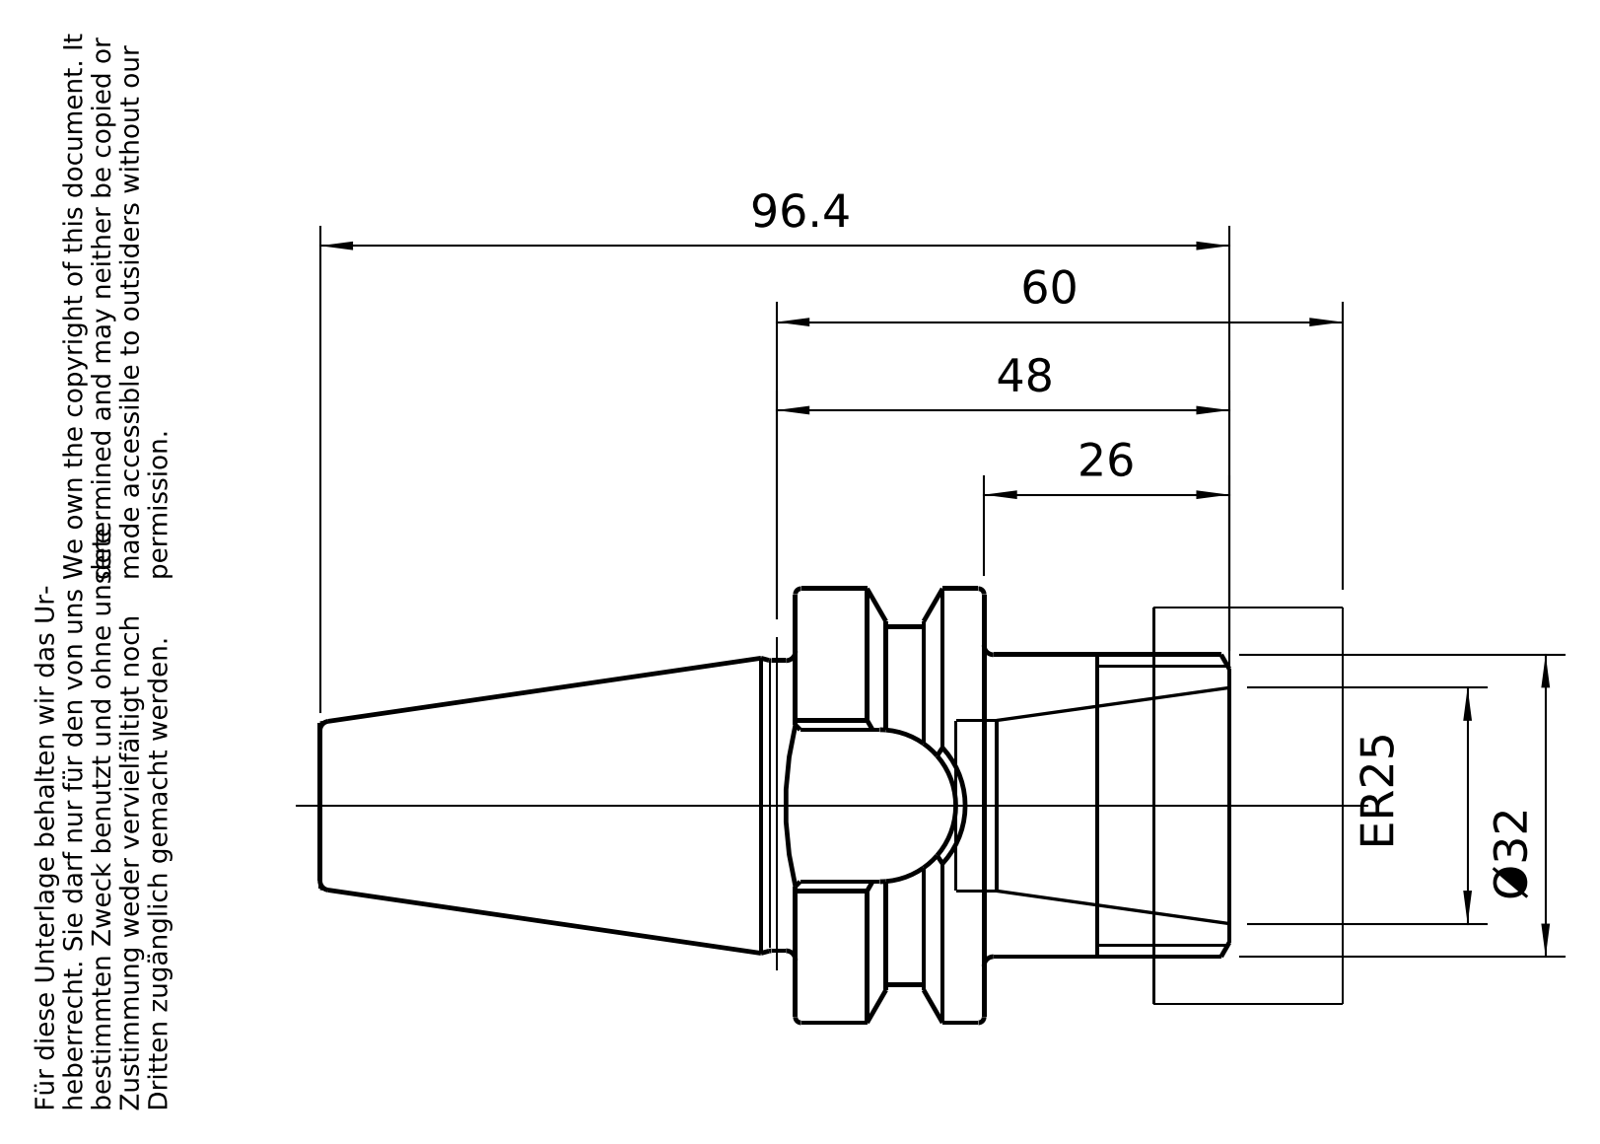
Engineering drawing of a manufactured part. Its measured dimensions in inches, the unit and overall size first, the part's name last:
Units: inches
Overall size (bounding box): 4.268 × 1.81 × 1.81
Round holes (diameter × count): ⌀0.398 ×1, ⌀0.493 ×1, ⌀0.512 ×1, ⌀0.709 ×1
Round bosses / shafts (diameter × count): ⌀1.81 ×1, ⌀1.654 ×1, ⌀1.26 ×1, ⌀1.211 ×1, ⌀0.473 ×1
Partial cylindrical surfaces — rounded edges, fillets, slot ends (radius × count): R0.319 ×1, R0.743 ×1
Main face-to-face distances: 0.787, 1.496, 0.709, 2.283, 1.811, 1.024, 0.315, 0.472, 0.669, 0.118
Volume: 5.246 in³ · Surface area: 32.96 in²
Bodies: 2 solids, 138 faces (46 planar, 24 cylindrical, 68 other)
Part name (STEP PRODUCT): 30-520-25; 83-912-25; 30-520-25_ASM
STEP written by: PRO/ENGINEER BY PARAMETRIC TECHNOLOGY CORPORATION, 2010430 (CONFIG_CONTROL_DESIGN)
